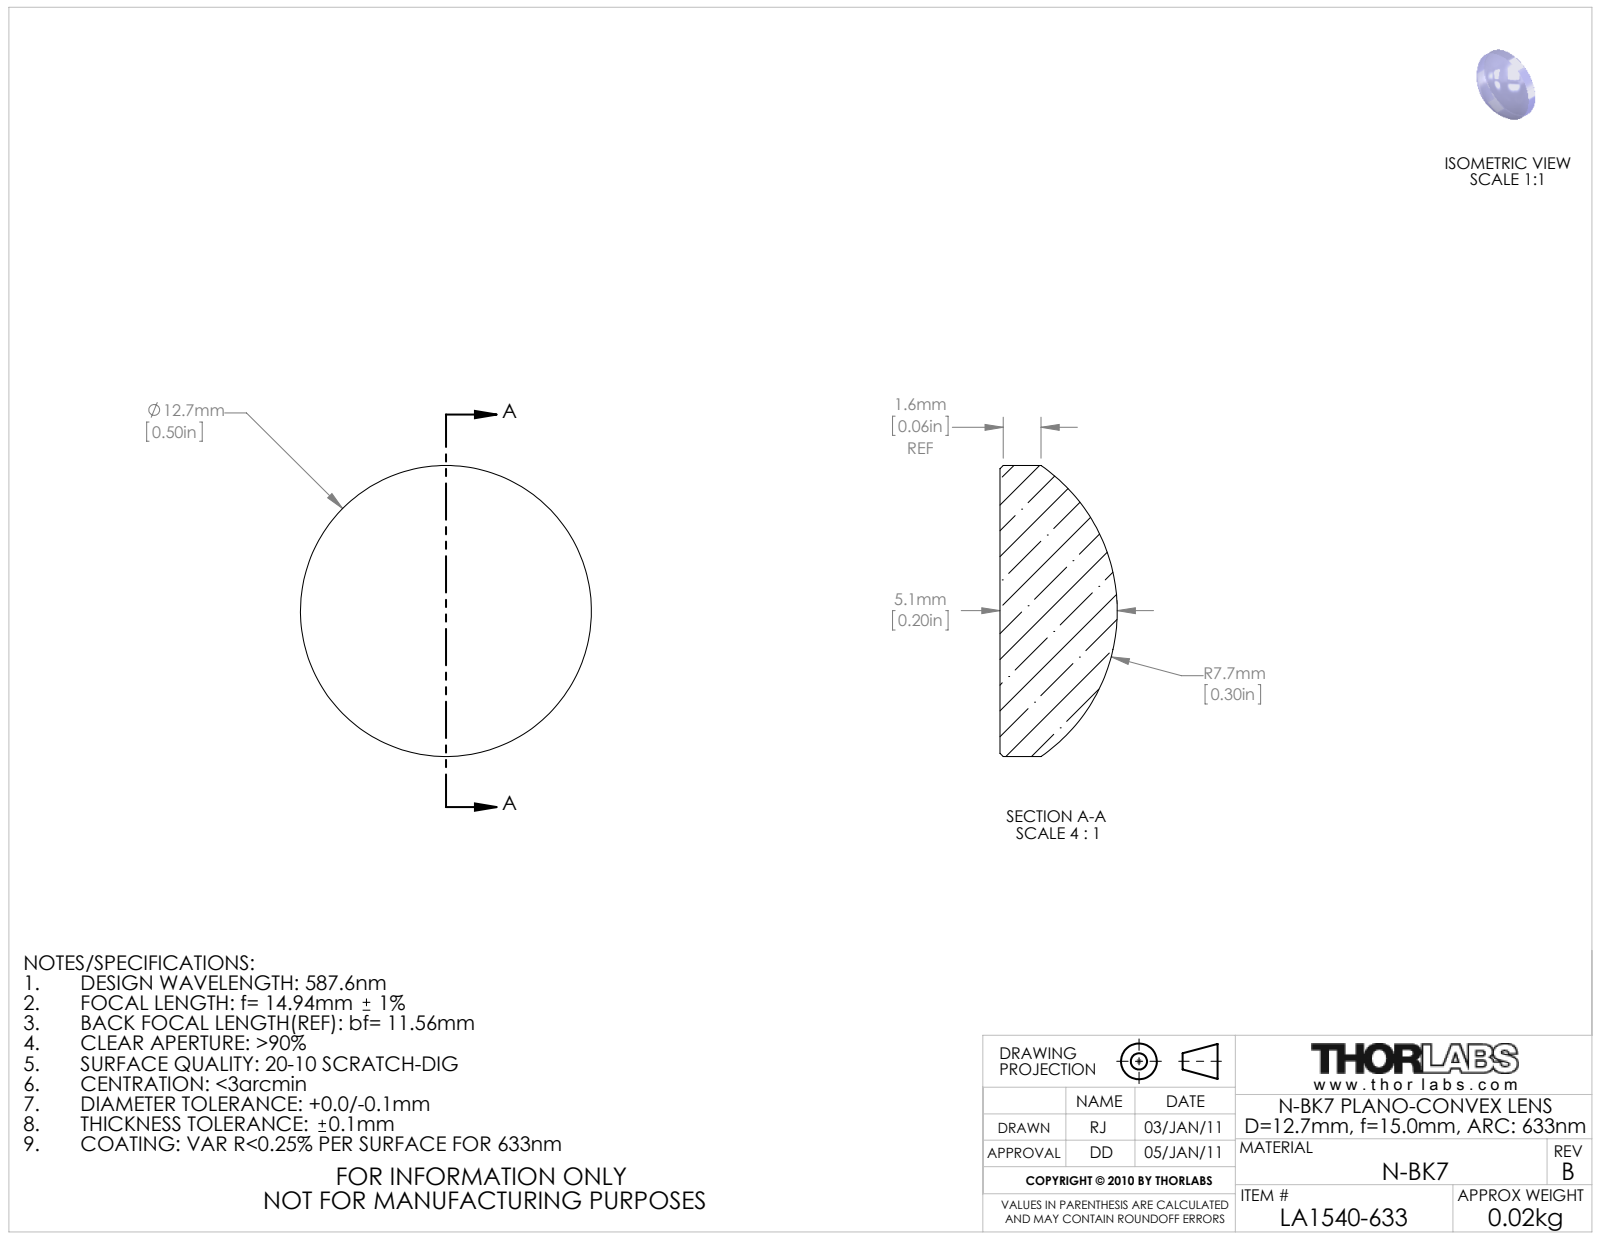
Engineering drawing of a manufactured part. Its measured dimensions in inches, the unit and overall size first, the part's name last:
Units: inches
Overall size (bounding box): 0.5 × 0.5 × 0.202
Round bosses / shafts (diameter × count): ⌀0.5 ×1
Bodies: 0 solids, 7 faces (1 planar, 2 cylindrical, 4 other)
Part name (STEP PRODUCT): 21774-E0W
STEP written by: SolidWorks 2011 (AUTOMOTIVE_DESIGN)
